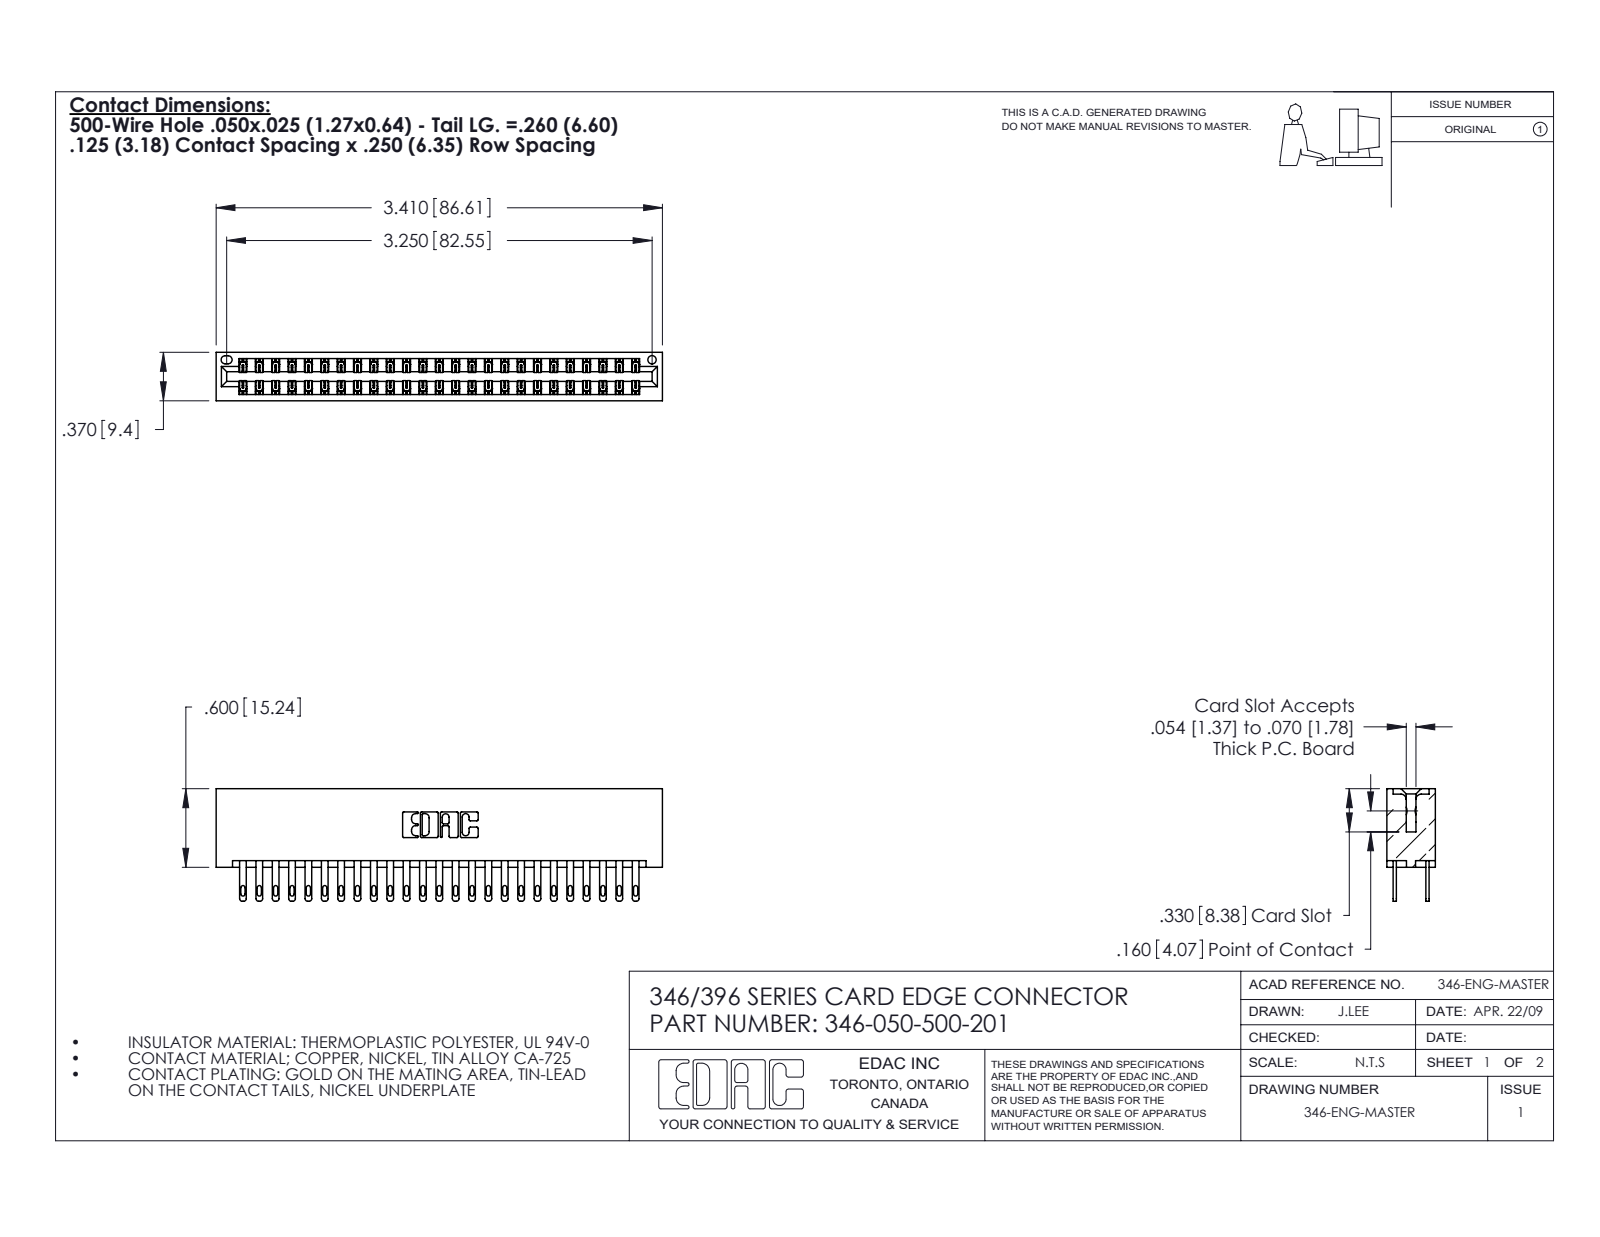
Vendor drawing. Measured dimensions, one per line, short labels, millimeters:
name: 345-292-001_345-293-100; 346 Part_No Mounting Lugs; 346-050-500-201
written by: SolidWorks 2020 (CONFIG_CONTROL_DESIGN)
unit: mm
bodies: 51 solids, 2514 faces (1522 planar, 992 cylindrical, 0 other)
size: 86.6 × 21.8 × 9.4
volume: 9 050 mm³; area: 12 850 mm²
holes: 1× ⌀1.6
rounds: 75× R0.2, 50× R0.4, 50× R0.5, 22× R0.3, 6× R0.2, 6× R0.8, 3× R0.7, 2× R0.4
face distances: 1.2, 8.2, 6.4, 1.8, 7.6, 0.6, 9.4, 7, 3.8, 5.6
